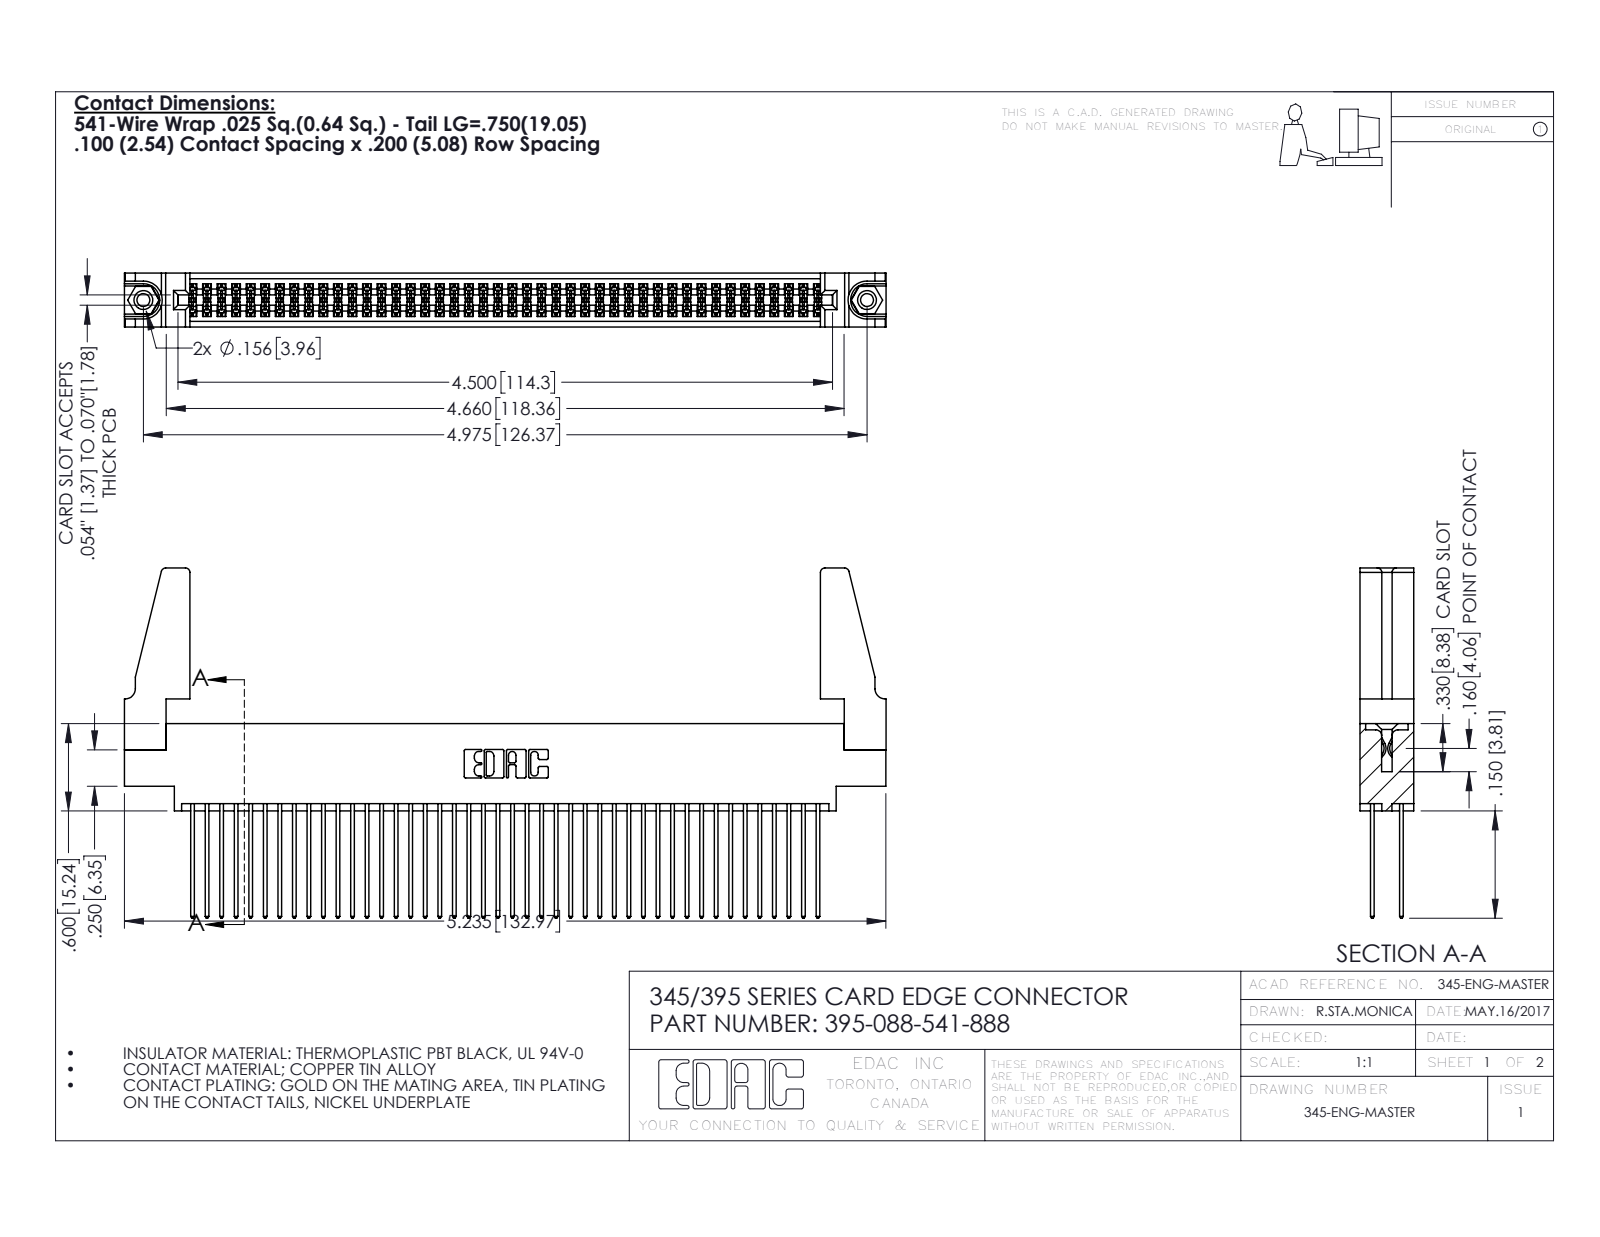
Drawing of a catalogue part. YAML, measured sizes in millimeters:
part_name: "345-220-078_345-220-088; 345 Part_0.170 Offset - 0.156 Dia-TH; 395-088-541-888; 345-292-001_345-293-141 (+1 more)"
step_written_by: "SolidWorks 2016 (CONFIG_CONTROL_DESIGN)"
units: millimeters
bodies: {solids: 93, faces: 4654, planar: 3060, cylindrical: 1578, other: 16}
overall_size: [133, 61.1, 9.4]
volume: 16580
surface_area: 25380
round_holes:
  - {diameter: 2.3, count: 2}
  - {diameter: 3.2, count: 2}
  - {diameter: 4, count: 2}
  - {diameter: 1.6, count: 1}
round_bosses_or_shafts:
  - {diameter: 3.9, count: 2}
partial_cylinders:
  - {radius: 0.2, count: 132}
  - {radius: 0.3, count: 88}
  - {radius: 0.3, count: 22}
  - {radius: 0.8, count: 8}
  - {radius: 0.2, count: 6}
  - {radius: 0.8, count: 6}
  - {radius: 0.7, count: 3}
  - {radius: 0.4, count: 2}
face_to_face_distances: [1.8, 7.6, 5.1, 2.5, 6.9, 0.6, 9.4, 5.7, 4.4, 3.8]
hole_center_spacings: [6.9, 120.4, 126.4]
